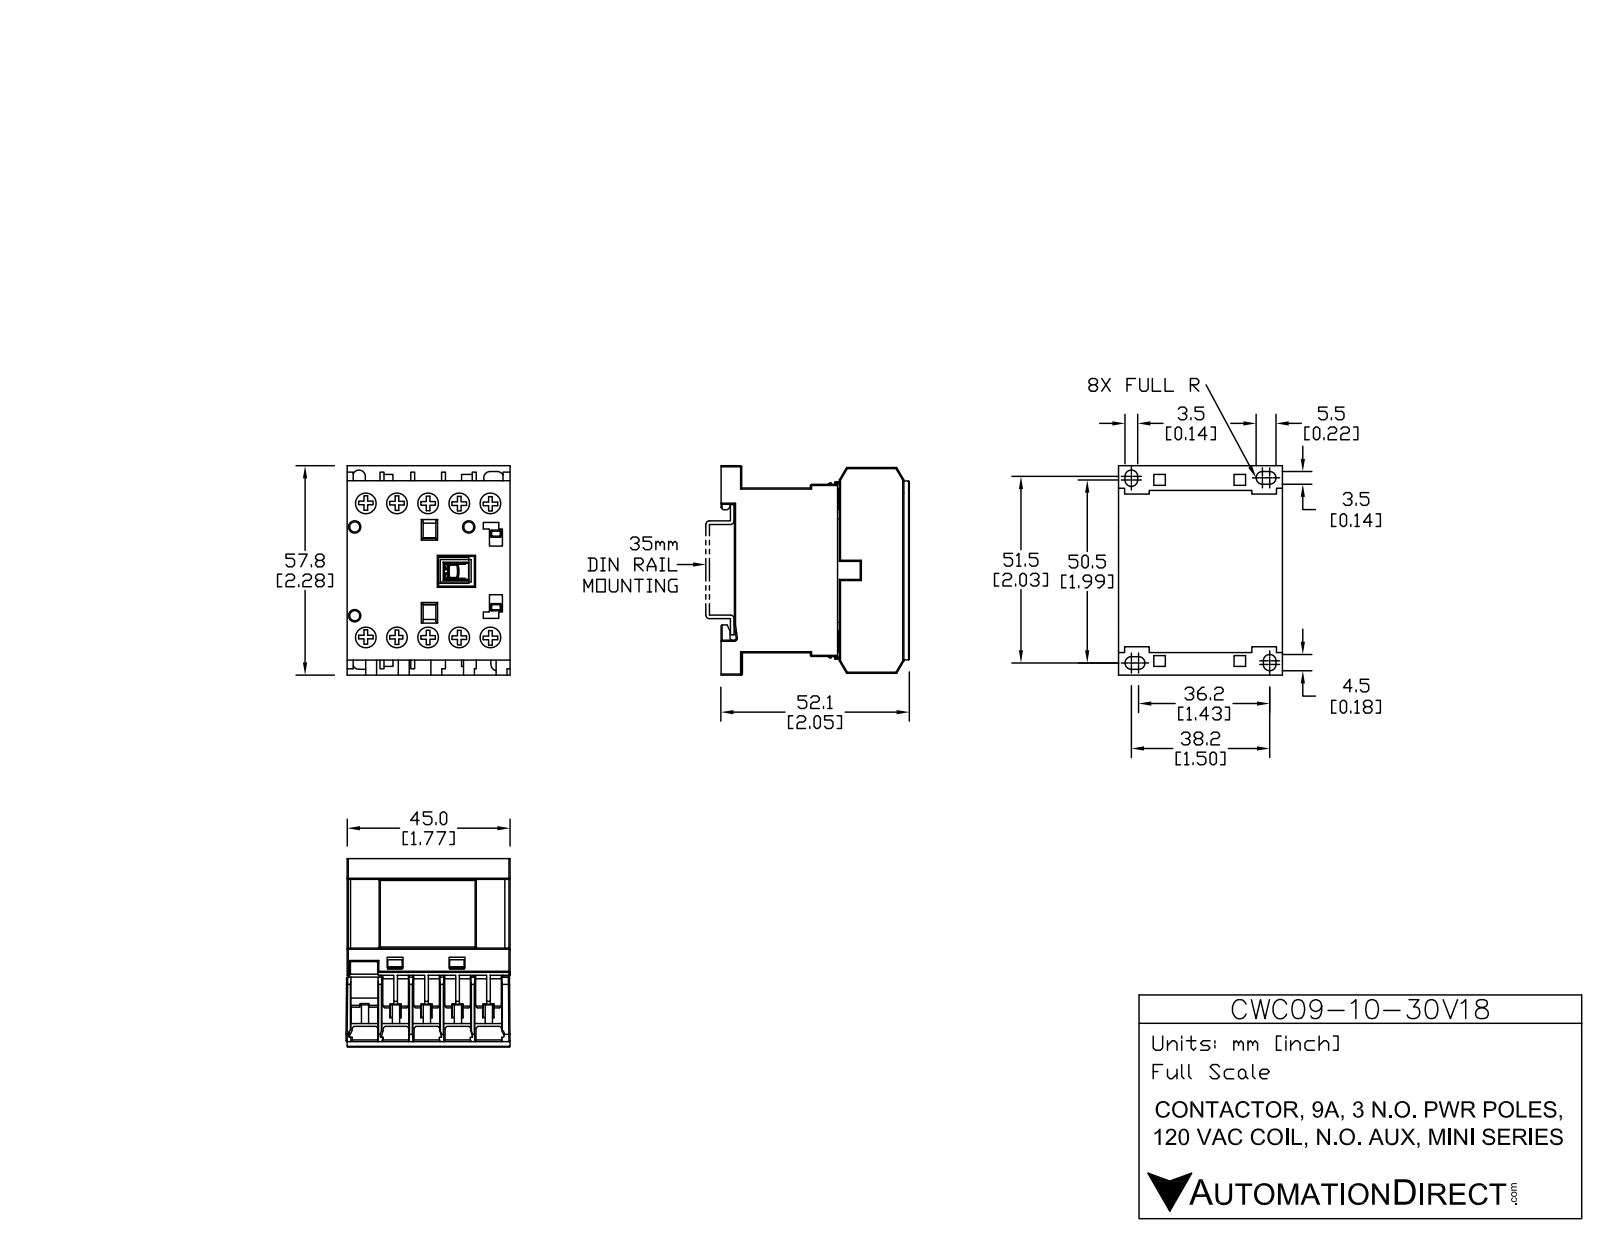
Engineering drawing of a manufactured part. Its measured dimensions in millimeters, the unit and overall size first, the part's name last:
Units: millimetres
Overall size (bounding box): 58.04 × 52.12 × 45.75
Round holes (diameter × count): ⌀6.2 ×10, ⌀2.8 ×3
Round bosses / shafts (diameter × count): ⌀5.9 ×10
Partial cylindrical surfaces — rounded edges, fillets, slot ends (radius × count): R0.3 ×20, R1.72 ×6, R1.73 ×2, R0.32 ×1, R0.42 ×1, R0.55 ×1
Main face-to-face distances: 8.25, 45.5, 1.25, 16.5, 9.5, 5.5, 17.75, 5.13, 10.63, 7
Hole centre spacings: 8.55, 37.94, 17.1, 40.72, 36.96, 25.65, 44.99, 6.91
Volume: 97 133 mm³ · Surface area: 30 437 mm²
Bodies: 15 solids, 535 faces (445 planar, 90 cylindrical, 0 other)
Part name (STEP PRODUCT): CWC09-10-30V18
STEP written by: SolidWorks 2013 (AUTOMOTIVE_DESIGN)
